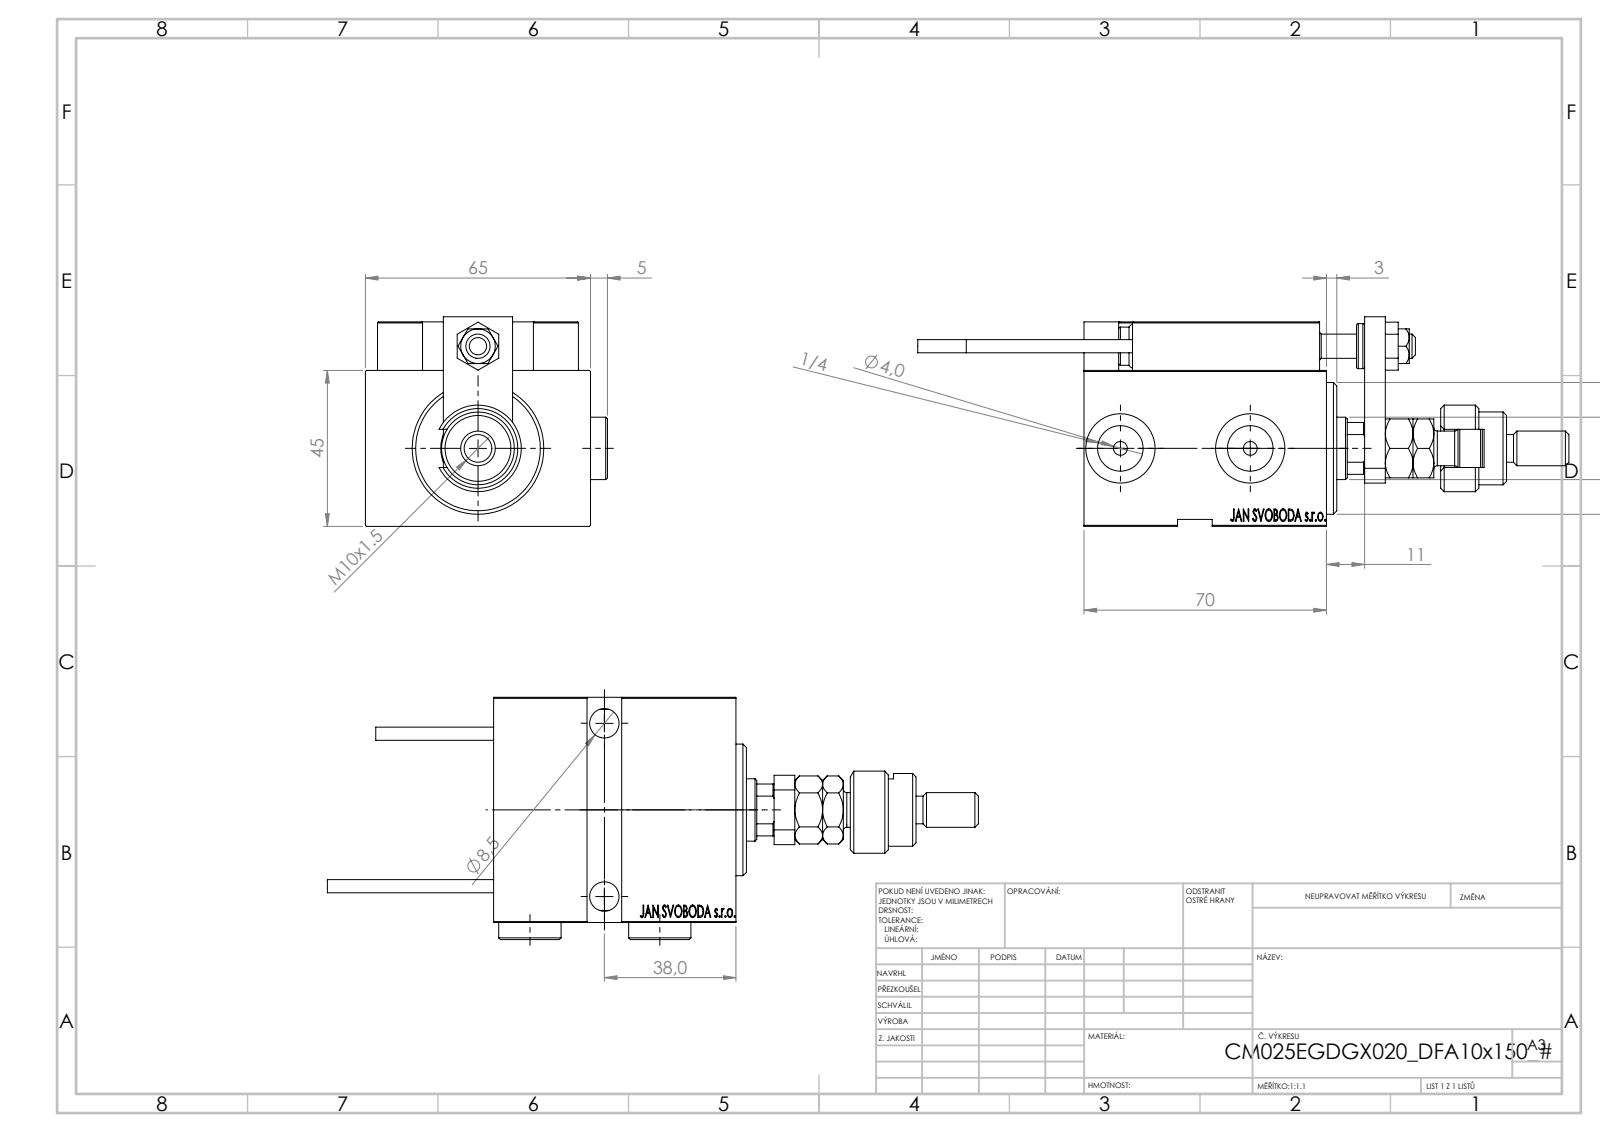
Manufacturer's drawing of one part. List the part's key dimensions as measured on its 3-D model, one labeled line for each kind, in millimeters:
Part name (STEP PRODUCT): FEMALE_PART_FOR_DFA; NUT_D10; Block; SWITCH DIM B,W (+8 more)
STEP written by: SolidWorks 2019 (CONFIG_CONTROL_DESIGN)
Units: millimetres
Bodies: 28 solids, 1422 faces (630 planar, 203 cylindrical, 589 other)
Overall size (bounding box): 188 × 69.9 × 60.5
Volume: 247 007 mm³ · Surface area: 71 783 mm²
Round holes (diameter × count): ⌀4 ×6, ⌀8 ×5, ⌀3.2 ×4, ⌀8.5 ×3, ⌀5 ×2, ⌀13.16 ×2, ⌀13.5 ×2, ⌀20 ×2, ⌀7 ×1, ⌀14.5 ×1, ⌀18 ×1, ⌀21.5 ×1
Round bosses / shafts (diameter × count): ⌀18 ×2, ⌀5 ×2, ⌀3.8 ×2, ⌀38 ×1, ⌀27 ×1, ⌀25 ×1, ⌀21 ×1, ⌀16 ×1
Partial cylindrical surfaces — rounded edges, fillets, slot ends (radius × count): R0.3 ×30, R3 ×2, R5.5 ×1, R8.5 ×1, R8.75 ×1
Main face-to-face distances: 45, 14, 65, 59, 6, 19, 3, 13, 8, 70
Hole centre spacings: 11.37, 20, 22.09, 29.59, 29.69, 30.89, 31.11, 34.17
